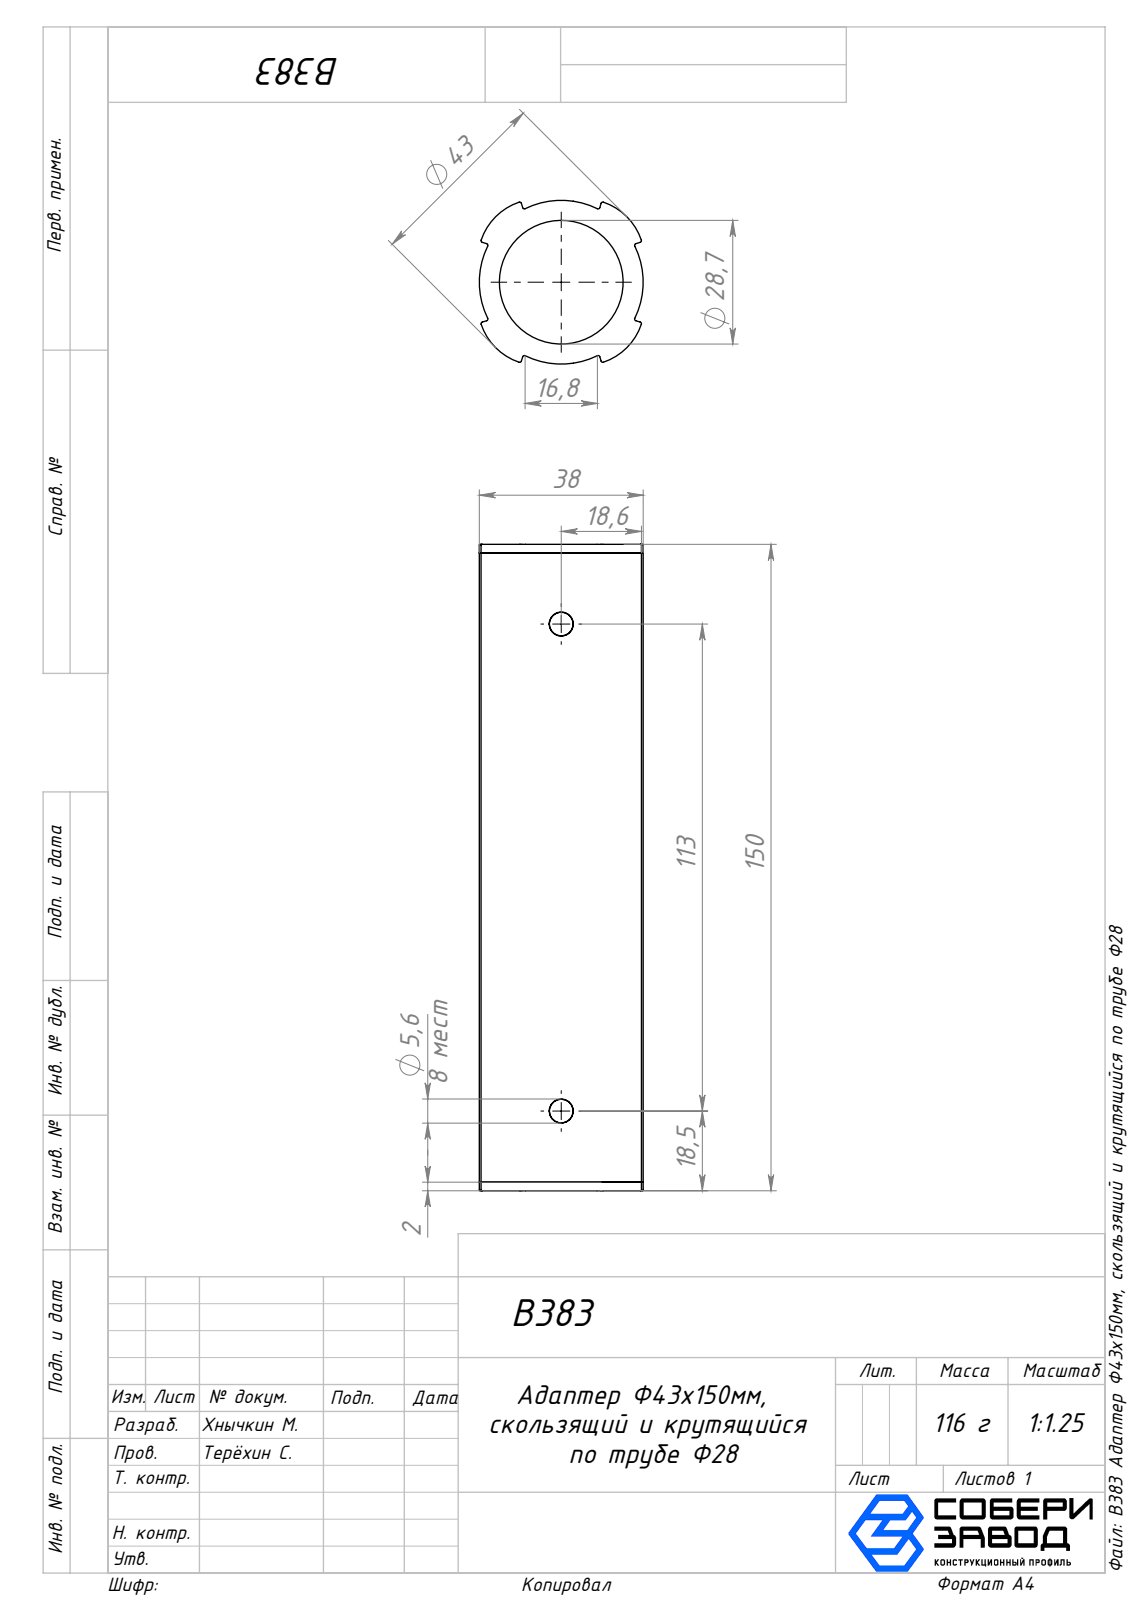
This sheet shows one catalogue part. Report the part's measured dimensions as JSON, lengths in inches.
{"part_name": "Корпус_00; Крышка_00; B383 Адаптер Ф43х150мм, скользящий и крутящийся по трубе Ф28", "step_written_by": "SolidWorks 2025 (AUTOMOTIVE_DESIGN)", "units": "inches", "bodies": {"solids": 3, "faces": 386, "planar": 96, "cylindrical": 208, "other": 82}, "overall_size": [5.906, 1.496, 1.496], "volume_in3": 2.882, "surface_area_in2": 73.39, "round_holes": [[0.22, 2], [1.13, 1], [1.181, 1]], "round_bosses_or_shafts": [[1.323, 1]], "partial_cylinders_radius": [[0.02, 20], [0.008, 16], [0.016, 16], [0.039, 12], [0.551, 4], [0.661, 2], [0.669, 1], [0.748, 1]], "face_to_face_distances": [0.079, 5.827, 0.811, 5.748, 5.906, 0.279, 0.279, 0.811, 0.374, 0.512], "hole_center_spacings": [4.449]}
